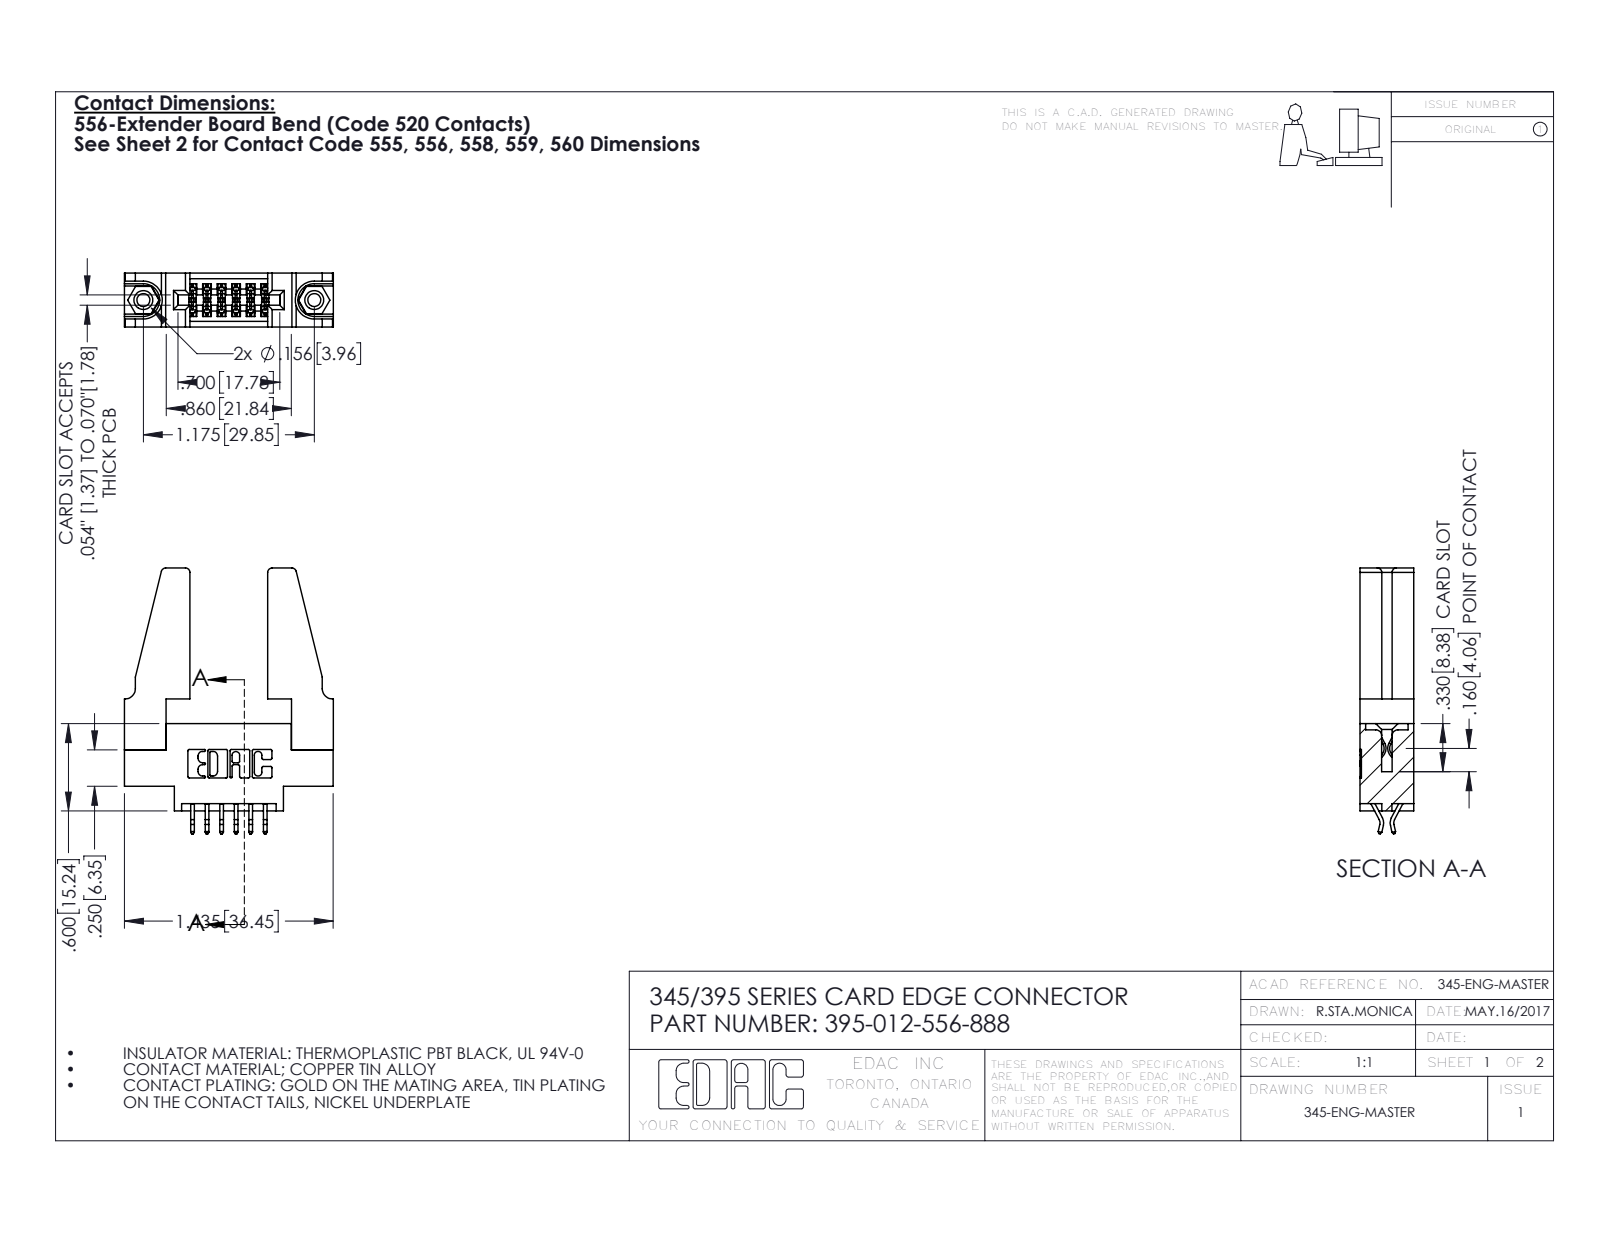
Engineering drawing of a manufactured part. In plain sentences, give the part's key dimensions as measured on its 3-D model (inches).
The part is named "345 Part_0.170 Offset - 0.156 Dia-TH; 395-012-556-888; 345-220-078_345-220-088; 345-250-001_345-250-001-102 (+1 more)". Its 3-D file was written by "SolidWorks 2016 (CONFIG_CONTROL_DESIGN)". It is 17 solids with 926 faces: 600 planar, 310 cylindrical and 16 other. Overall it measures 1.827 by 1.436 by 0.37 inches. Its volume is 0.387 cubic inches and its surface area 11.06 square inches. Round holes: 2 of diameter 0.089, 2 of diameter 0.125, 2 of diameter 0.156, 1 of diameter 0.064. Round bosses or shafts: 2 of diameter 0.155. Partial cylindrical surfaces (rounded edges, fillets, slot ends): 22 of radius 0.01, 18 of radius 0.006, 8 of radius 0.03, 6 of radius 0.007, 6 of radius 0.031, 3 of radius 0.026, 2 of radius 0.01, 2 of radius 0.014. The main face-to-face distances are 0.37, 0.072, 0.298, 0.2, 0.15, 0.148, 0.225, 0.025, 0.098, 0.272. The hole center spacings are 0.27, 0.946, 1.175.
